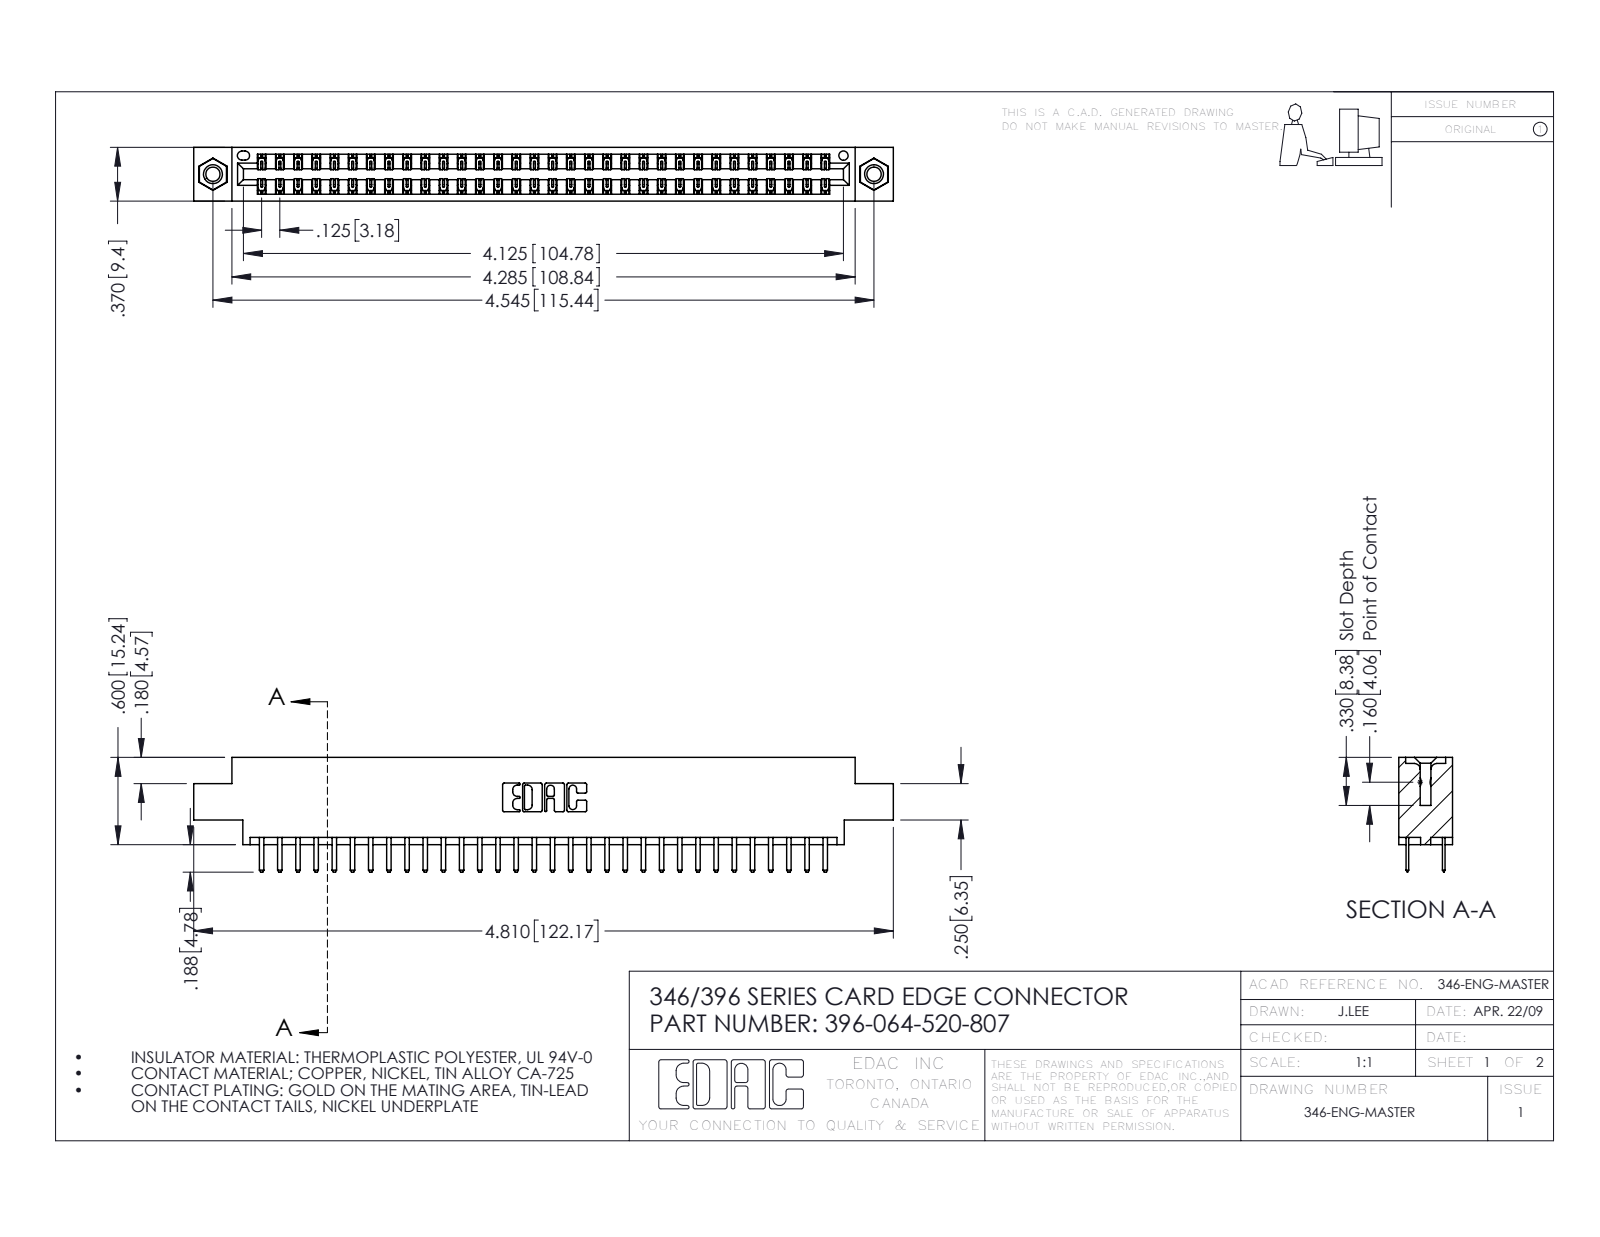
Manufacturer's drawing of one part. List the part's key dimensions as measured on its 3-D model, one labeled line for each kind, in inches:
Part name (STEP PRODUCT): 346 Part_0.170 Offset - 0.156 Dia-TI; 345-292-001_345-293-120; 345-250-001_345-250-005-103; 396-064-520-807
STEP written by: SolidWorks 2016 (CONFIG_CONTROL_DESIGN)
Units: inches
Bodies: 67 solids, 3770 faces (2480 planar, 1274 cylindrical, 16 other)
Overall size (bounding box): 4.81 × 0.788 × 0.37
Volume: 0.71 in³ · Surface area: 24.78 in²
Round holes (diameter × count): ⌀0.098 ×2, ⌀0.125 ×2, ⌀0.156 ×2, ⌀0.064 ×1
Round bosses / shafts (diameter × count): ⌀0.155 ×2
Partial cylindrical surfaces — rounded edges, fillets, slot ends (radius × count): R0.006 ×96, R0.01 ×68, R0.01 ×22, R0.007 ×6, R0.031 ×6, R0.026 ×3, R0.014 ×2, R0.022 ×2
Main face-to-face distances: 0.048, 0.322, 0.37, 0.25, 0.275, 0.072, 0.298, 0.025, 0.222, 0.148
Hole centre spacings: 0.246, 4.337, 4.545
